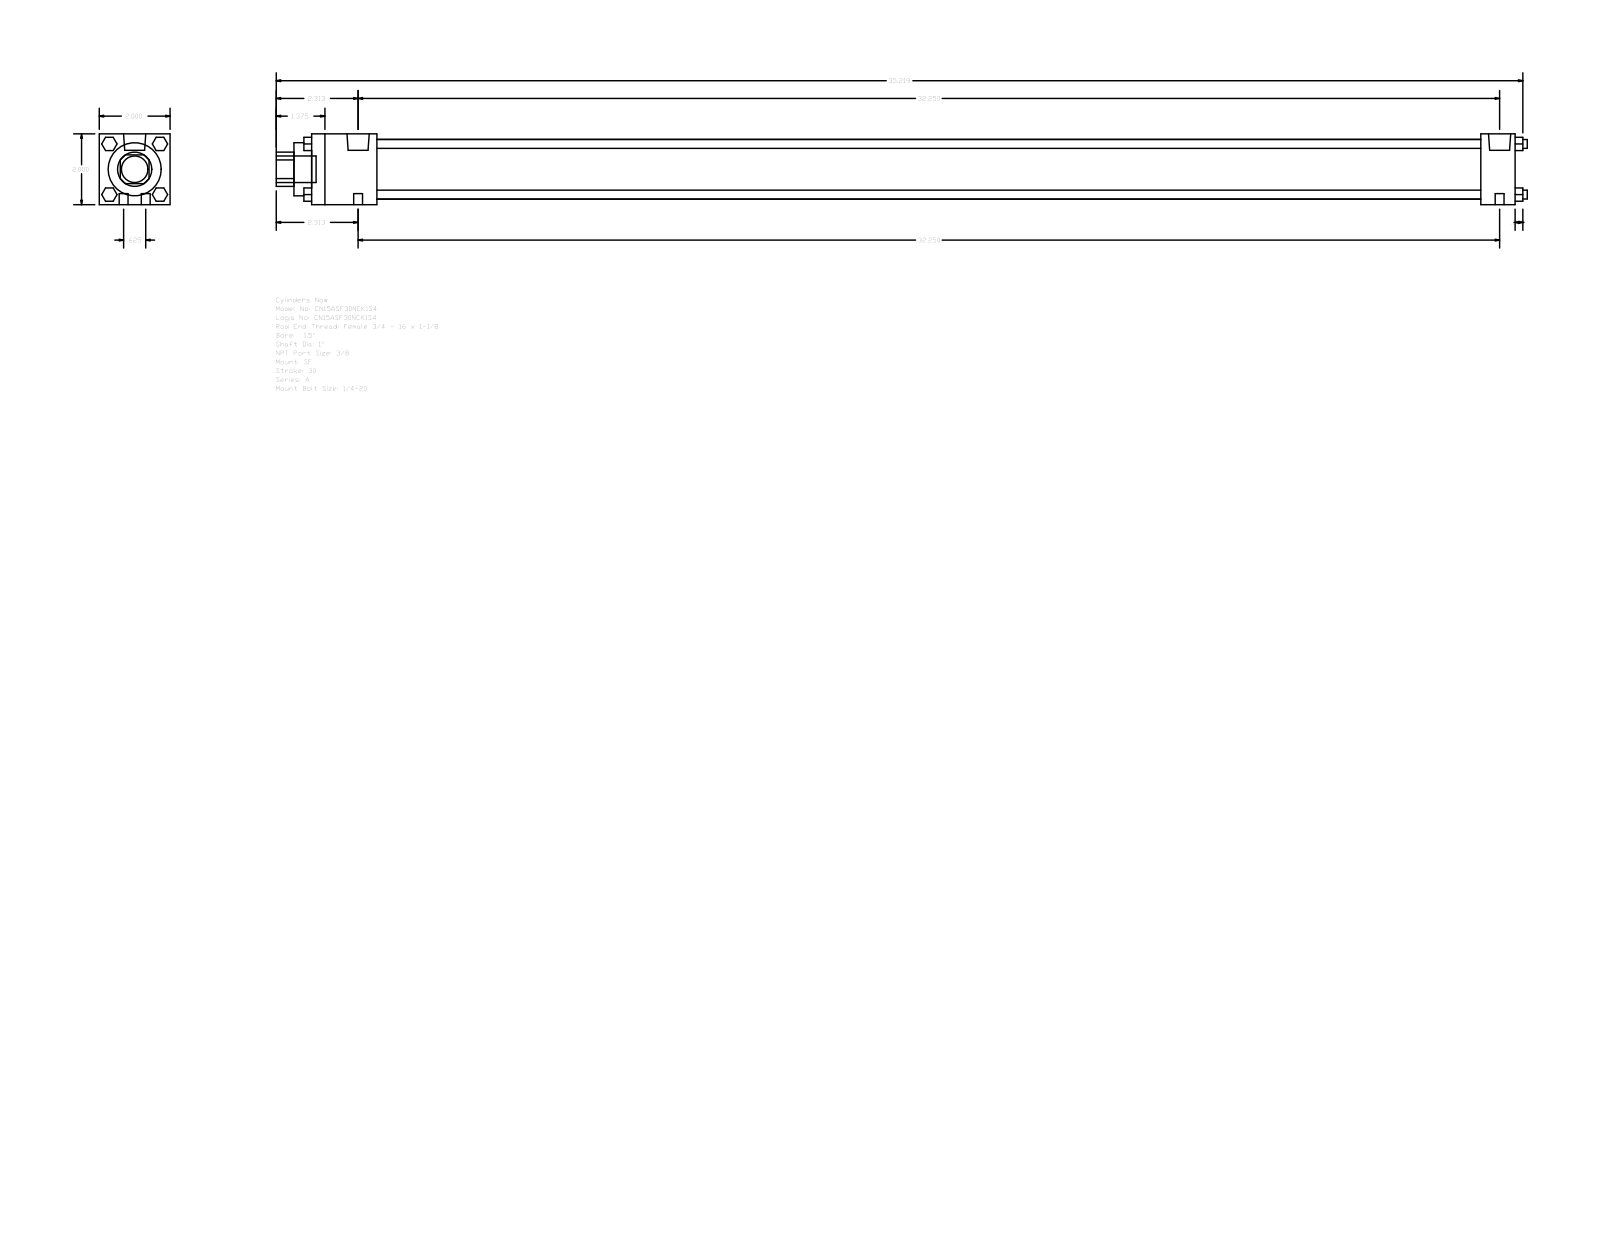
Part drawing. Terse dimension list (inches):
name: A_SF__0150_1
written by: GSSL Pune (CONFIG_CONTROL_DESIGN)
unit: in
bodies: 0 solids, 124 faces (94 planar, 30 cylindrical, 0 other)
size: 35.344 × 2 × 2
holes: 1× ⌀1, 1× ⌀1.5, 1× ⌀1.69
bosses: 8× ⌀0.25, 2× ⌀0.627, 2× ⌀0.219, 1× ⌀0.75
rounds: 1× R0.484
face distances: 2, 34, 1.844, 33.031, 31.187, 32.156, 0.969, 0.5, 2.344, 33.531
